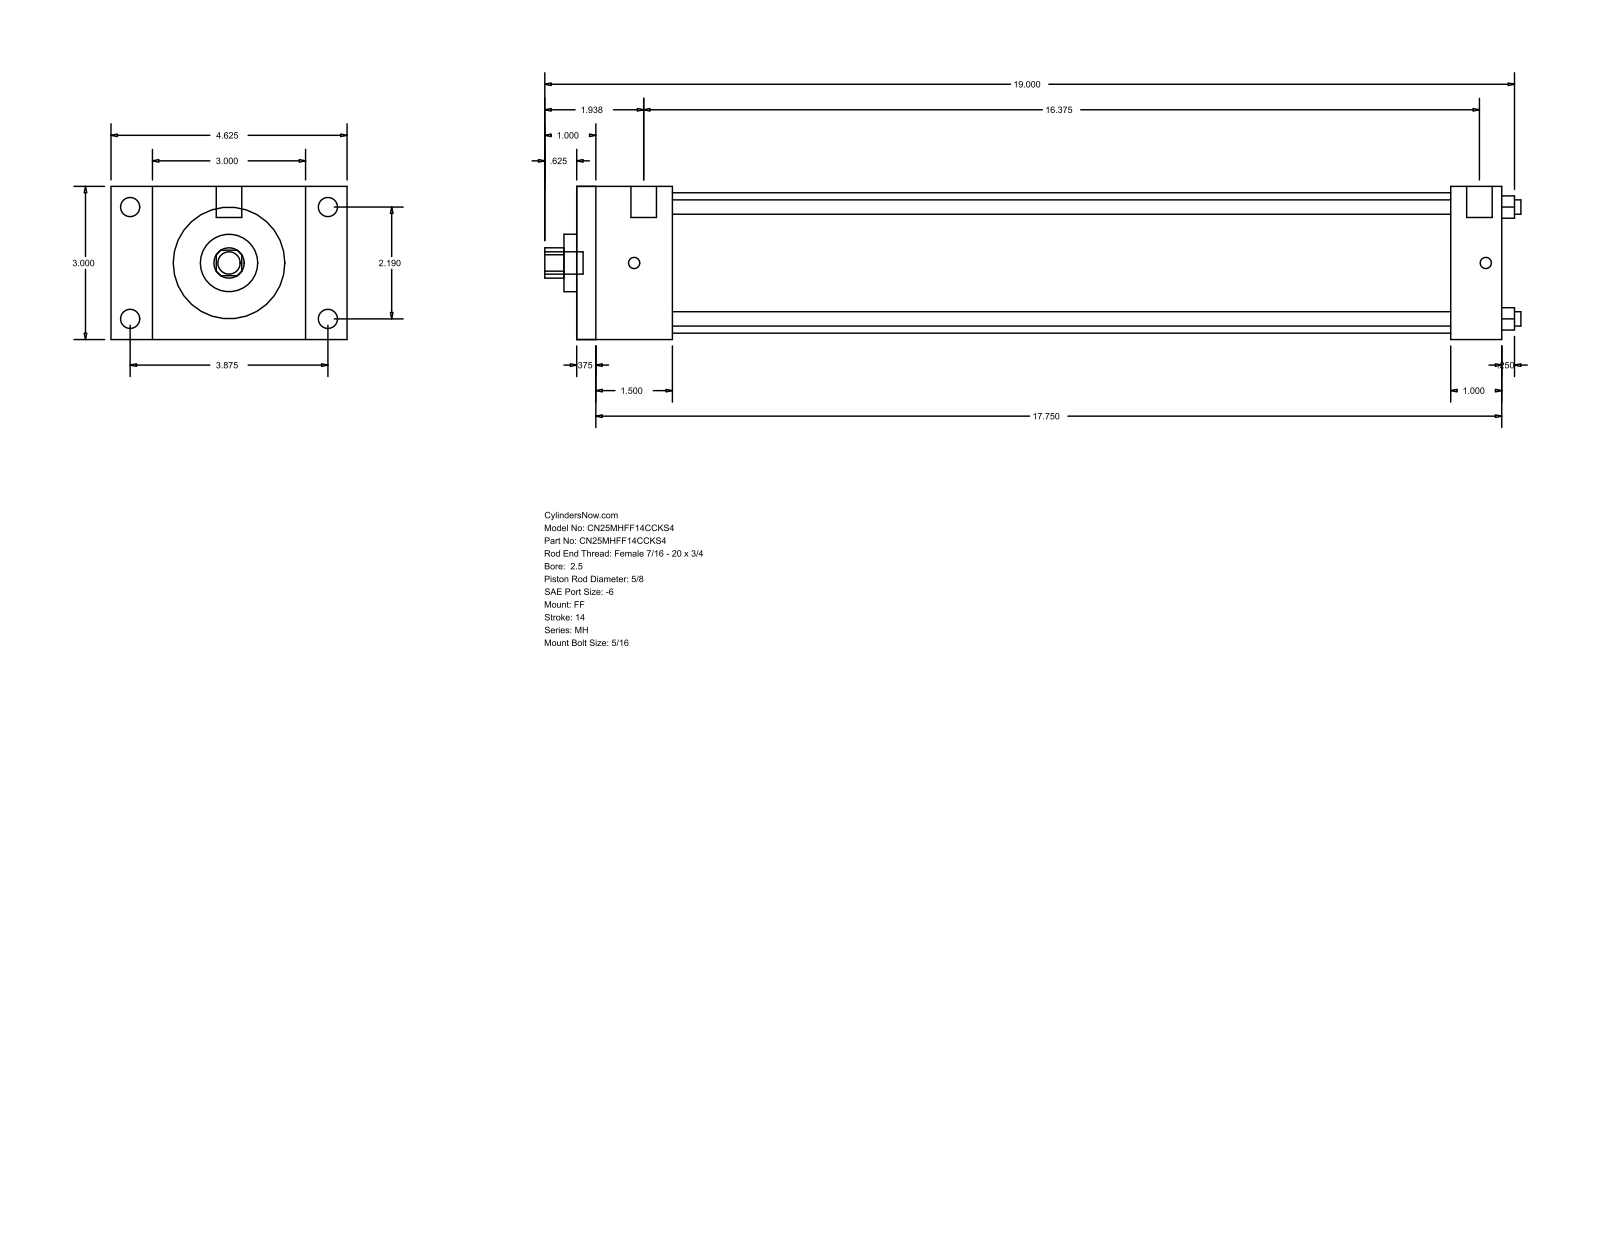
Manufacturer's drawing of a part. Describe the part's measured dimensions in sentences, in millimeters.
The part is named "MH_FF__0250_0.625". Its 3-D file was written by "GSSL Pune (CONFIG_CONTROL_DESIGN)". It is 0 solids with 92 faces: 64 planar, 28 cylindrical and 0 other. Overall it measures 485.77 by 117.47 by 76.2 millimeters. Round holes: 4 of diameter 7.14, 1 of diameter 15.88, 1 of diameter 28.57, 1 of diameter 69.85. Round bosses or shafts: 4 of diameter 9.53, 4 of diameter 5.56, 2 of diameter 12.7, 1 of diameter 11.11. Partial cylindrical surfaces (rounded edges, fillets, slot ends): 1 of radius 7.54. The main face-to-face distances are 76.2, 460.37, 9.52, 450.85, 25.4, 47.62, 434.97, 38.1, 425.45, 387.35. The hole center spacings are 39.33, 55.62, 78.66.
